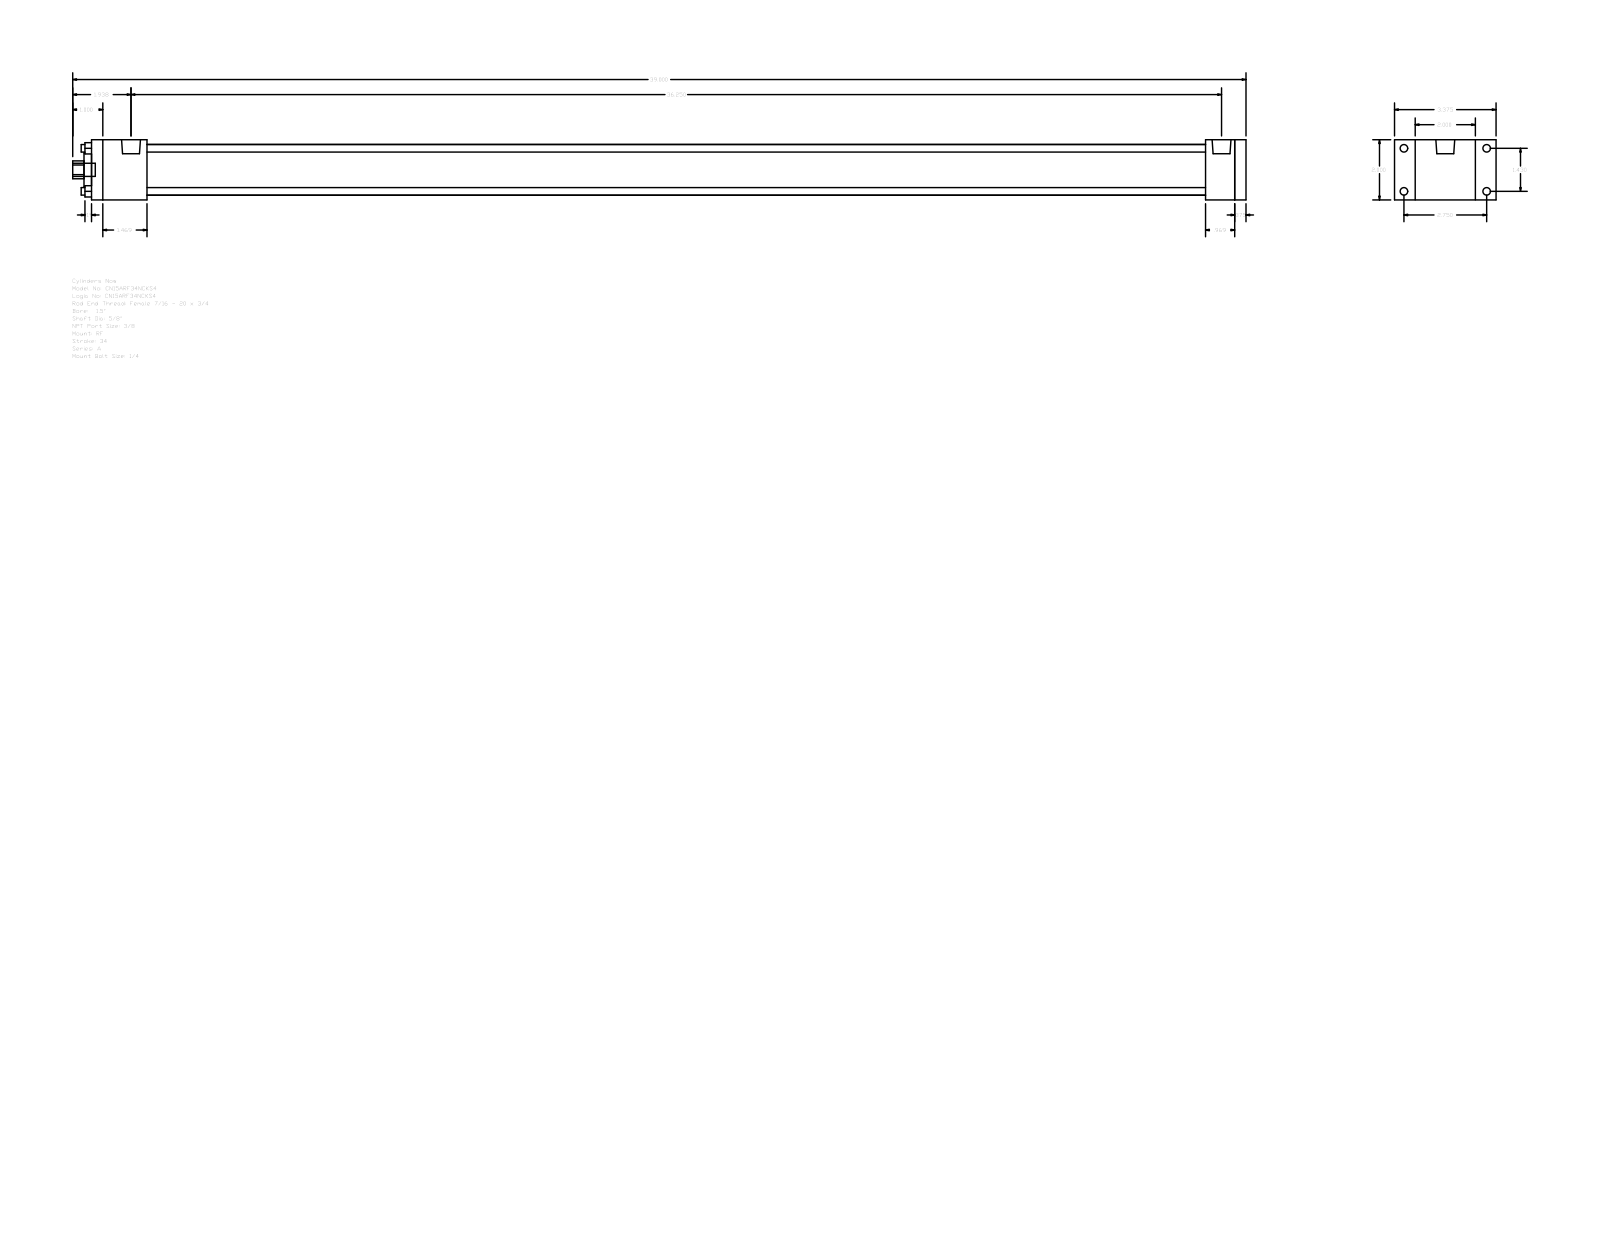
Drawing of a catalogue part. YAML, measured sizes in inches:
part_name: "A_RF__0150_0.625"
step_written_by: "GSSL Pune (CONFIG_CONTROL_DESIGN)"
units: inches
bodies: {solids: 0, faces: 92, planar: 64, cylindrical: 28, other: 0}
overall_size: [39, 3.375, 2]
round_holes:
  - {diameter: 0.25, count: 4}
  - {diameter: 0.625, count: 1}
  - {diameter: 1.125, count: 1}
  - {diameter: 1.69, count: 1}
round_bosses_or_shafts:
  - {diameter: 0.25, count: 4}
  - {diameter: 0.219, count: 4}
  - {diameter: 0.627, count: 2}
  - {diameter: 0.437, count: 1}
partial_cylinders:
  - {radius: 0.297, count: 1}
face_to_face_distances: [2, 0.375, 38, 38.375, 37.031, 0.969, 1.344, 1.844, 35.187, 36.156]
hole_center_spacings: [1.011, 1.43, 2.022]
